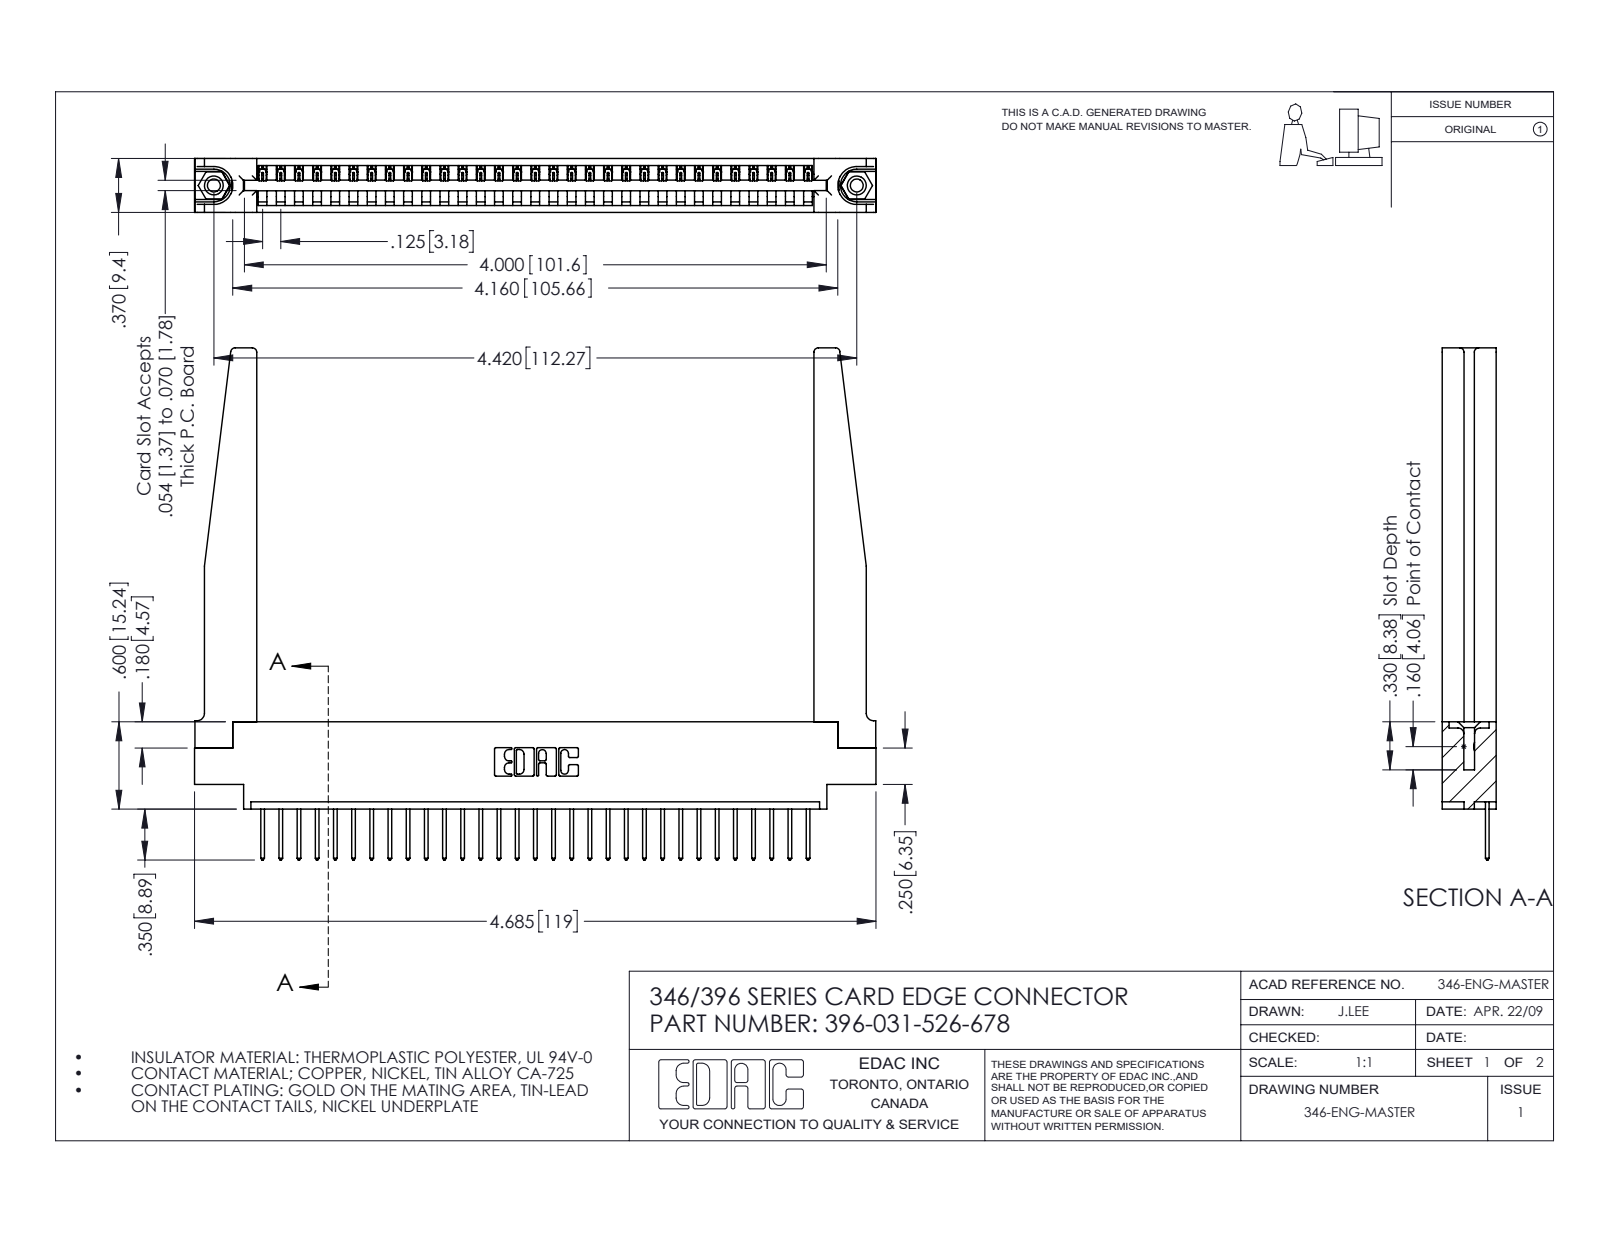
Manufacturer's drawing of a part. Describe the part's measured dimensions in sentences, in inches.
The part is named "345-292-001_345-293-126; 346-220-078_345-220-078; 346 Part_0.170 Offset - 0.156 Dia-TH; 345-250-001_345-250-001-102 (+1 more)". Its 3-D file was written by "SolidWorks 2016 (CONFIG_CONTROL_DESIGN)". It is 36 solids with 2158 faces: 1462 planar, 644 cylindrical and 52 other. Overall it measures 4.685 by 3.52 by 0.37 inches. Its volume is 1.101 cubic inches and its surface area 31.73 square inches. Round holes: 2 of diameter 0.089, 2 of diameter 0.125, 2 of diameter 0.156, 1 of diameter 0.064. Round bosses or shafts: 2 of diameter 0.155. Partial cylindrical surfaces (rounded edges, fillets, slot ends): 62 of radius 0.006, 62 of radius 0.01, 22 of radius 0.01, 8 of radius 0.03, 6 of radius 0.007, 6 of radius 0.031, 3 of radius 0.026, 2 of radius 0.031. The main face-to-face distances are 0.37, 0.048, 0.322, 0.072, 0.148, 0.15, 0.25, 0.298, 0.025, 0.222. The hole center spacings are 0.246, 4.212, 4.42.
